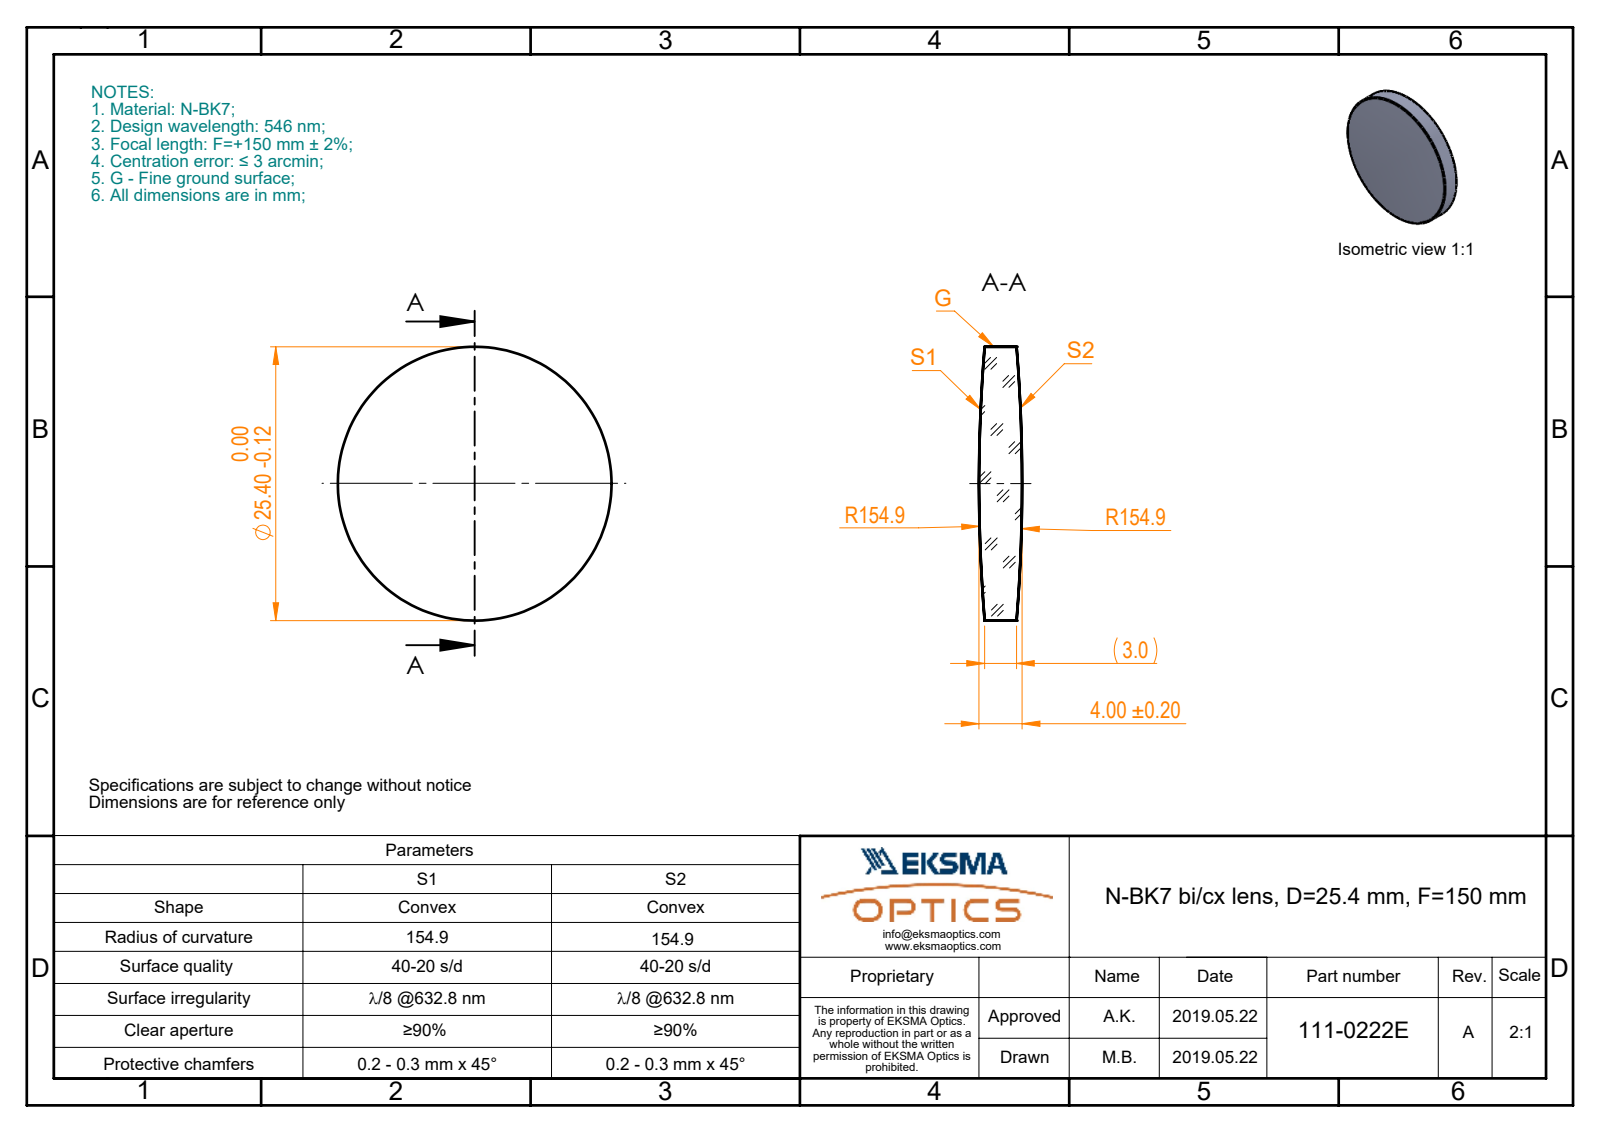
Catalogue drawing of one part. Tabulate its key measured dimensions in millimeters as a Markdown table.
| quantity | value |
| --- | --- |
| part name | 111-0222E BK7 bi-cx 25.4 F150 |
| STEP written by | SolidWorks 2017 (CONFIG_CONTROL_DESIGN) |
| units | millimeters |
| bodies | 1 solid, 6 faces (0 planar, 2 cylindrical, 4 other) |
| overall size | 25.4 × 25.4 × 4 |
| volume | 1 763 mm³ |
| surface area | 1 251 mm² |
| round bosses / shafts (diameter × count) | 25.4 × 1 |
